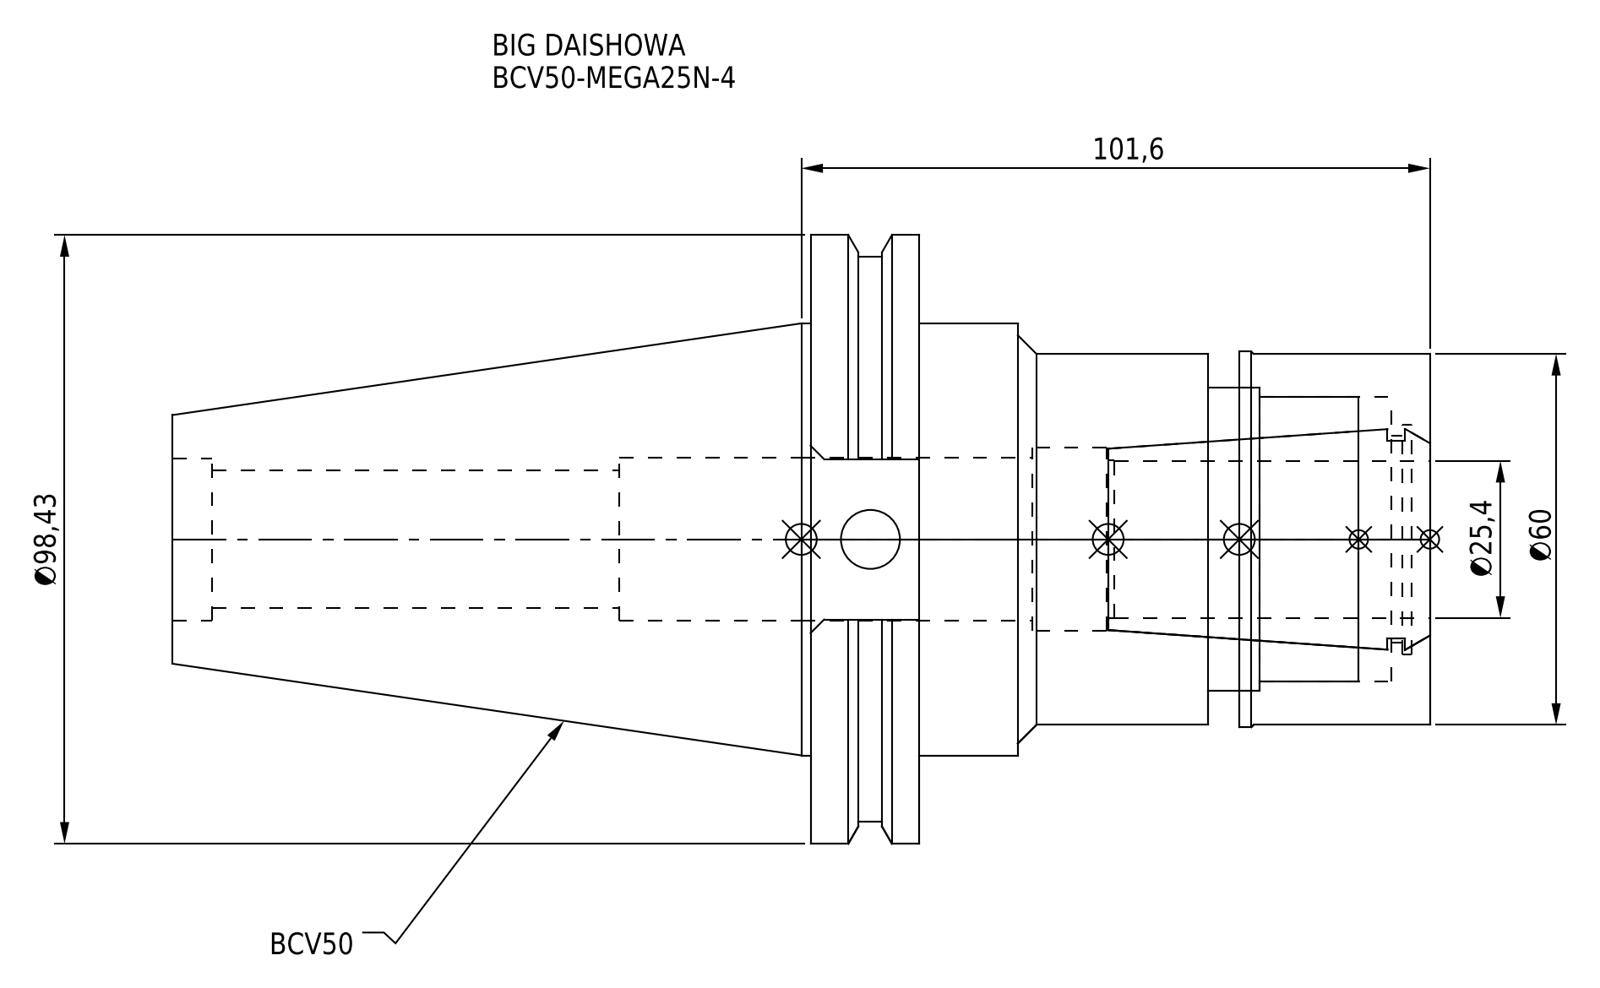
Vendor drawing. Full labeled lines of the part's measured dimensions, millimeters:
Part name (STEP PRODUCT): BCV50MN25040-254_ASM.stp; BCV50-MEGA25N-4; MGN25_1.stp; BCV50-MEGA25N-4-254-FreeParts (+3 more)
STEP written by: SolidWorks 2019 (CONFIG_CONTROL_DESIGN)
Units: millimetres
Bodies: 2 solids, 86 faces (32 planar, 40 cylindrical, 14 other)
Overall size (bounding box): 203.2 × 98.42 × 94.95
Volume: 495 467 mm³ · Surface area: 78 588 mm²
Round holes (diameter × count): ⌀9.53 ×1, ⌀22.3 ×1, ⌀26.23 ×1, ⌀26.3 ×1, ⌀29.6 ×1, ⌀33.5 ×1, ⌀37.2 ×1, ⌀46 ×1, ⌀49 ×1
Round bosses / shafts (diameter × count): ⌀98.42 ×1, ⌀91.29 ×1, ⌀69.85 ×1, ⌀60.7 ×1, ⌀60 ×1
Main face-to-face distances: 17.55, 82.55, 100.1, 35.9, 64.2, 30.8, 51.75, 69.3, 5.1, 46.65
